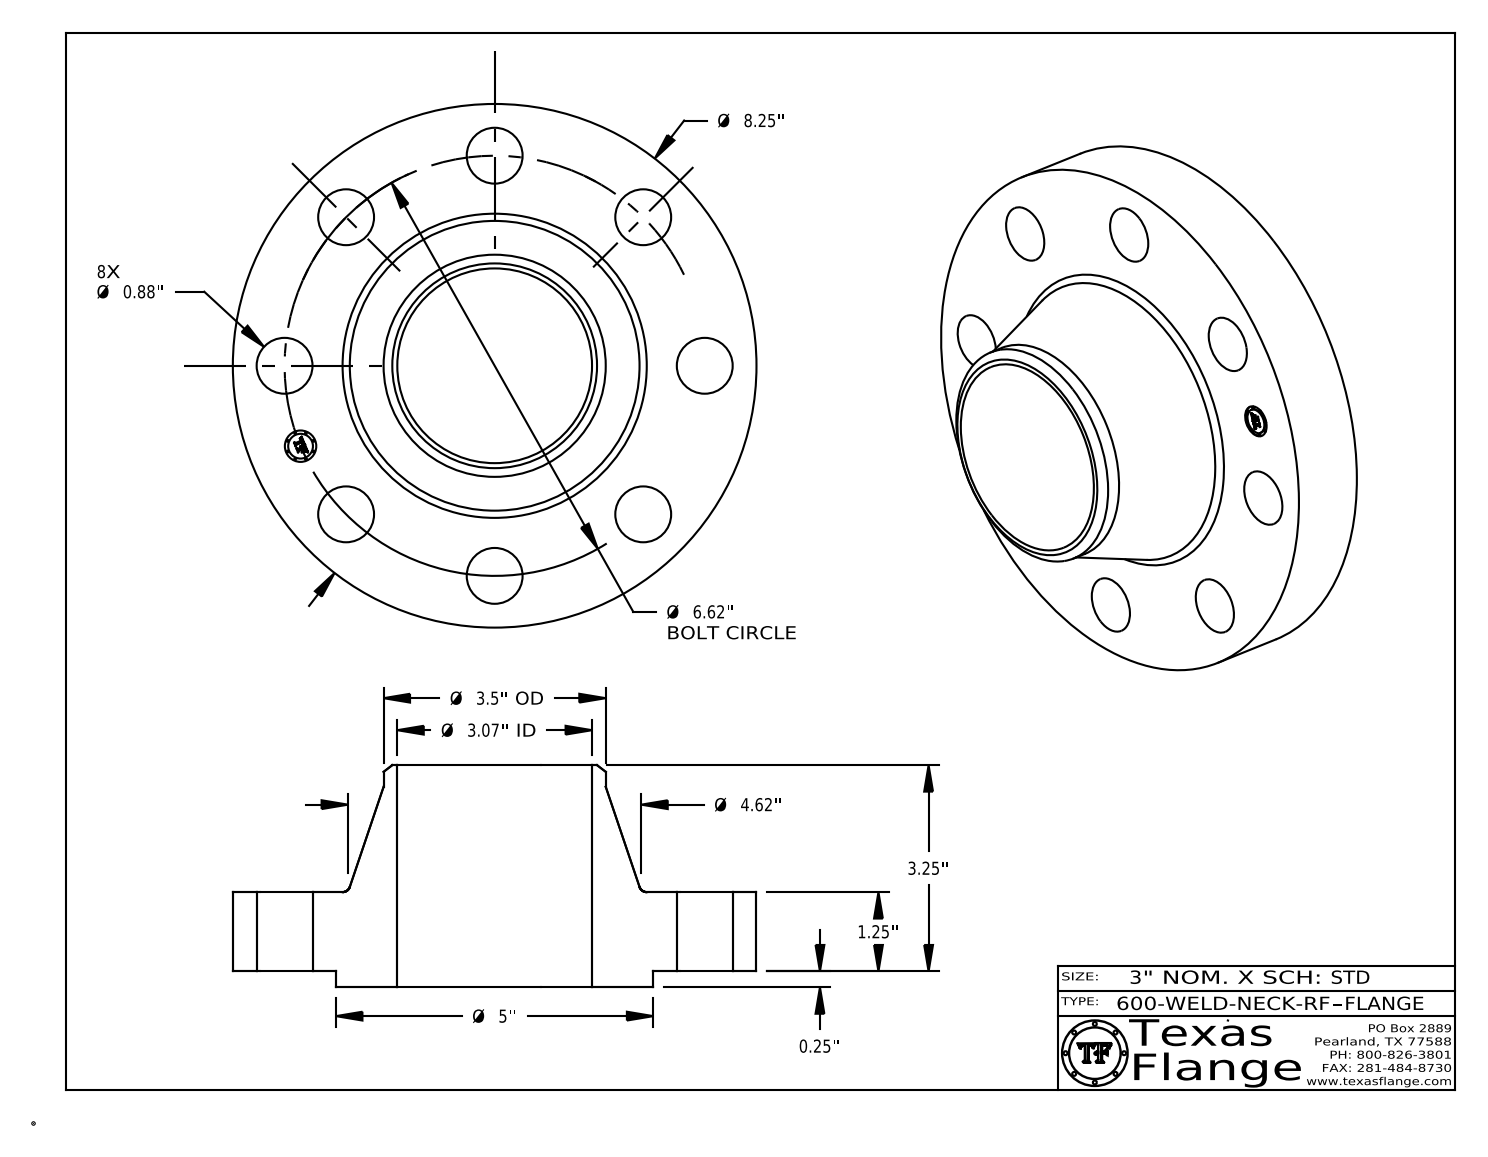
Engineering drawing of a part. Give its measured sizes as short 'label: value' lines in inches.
name: 600-WELD-NECK-RF
written by: CATIA V5 STEP AP214 (AUTOMOTIVE_DESIGN)
unit: in
bodies: 1 solid, 419 faces (369 planar, 44 cylindrical, 6 other)
size: 8.25 × 8.25 × 3.5
volume: 64.61 in³; area: 198 in²
holes: 8× ⌀0.88, 1× ⌀0.495, 1× ⌀3.068
bosses: 8× ⌀0.03, 1× ⌀8.25, 1× ⌀5, 1× ⌀3.5, 1× ⌀0.39
face distances: 1.25, 0.25, 1.5, 3.5, 3.25, 2, 0.015, 1.485, 1.235, 2.015
hole spacings: 3.31, 2.533, 6.116, 4.681, 4.681, 1.291, 3.678, 6.493
